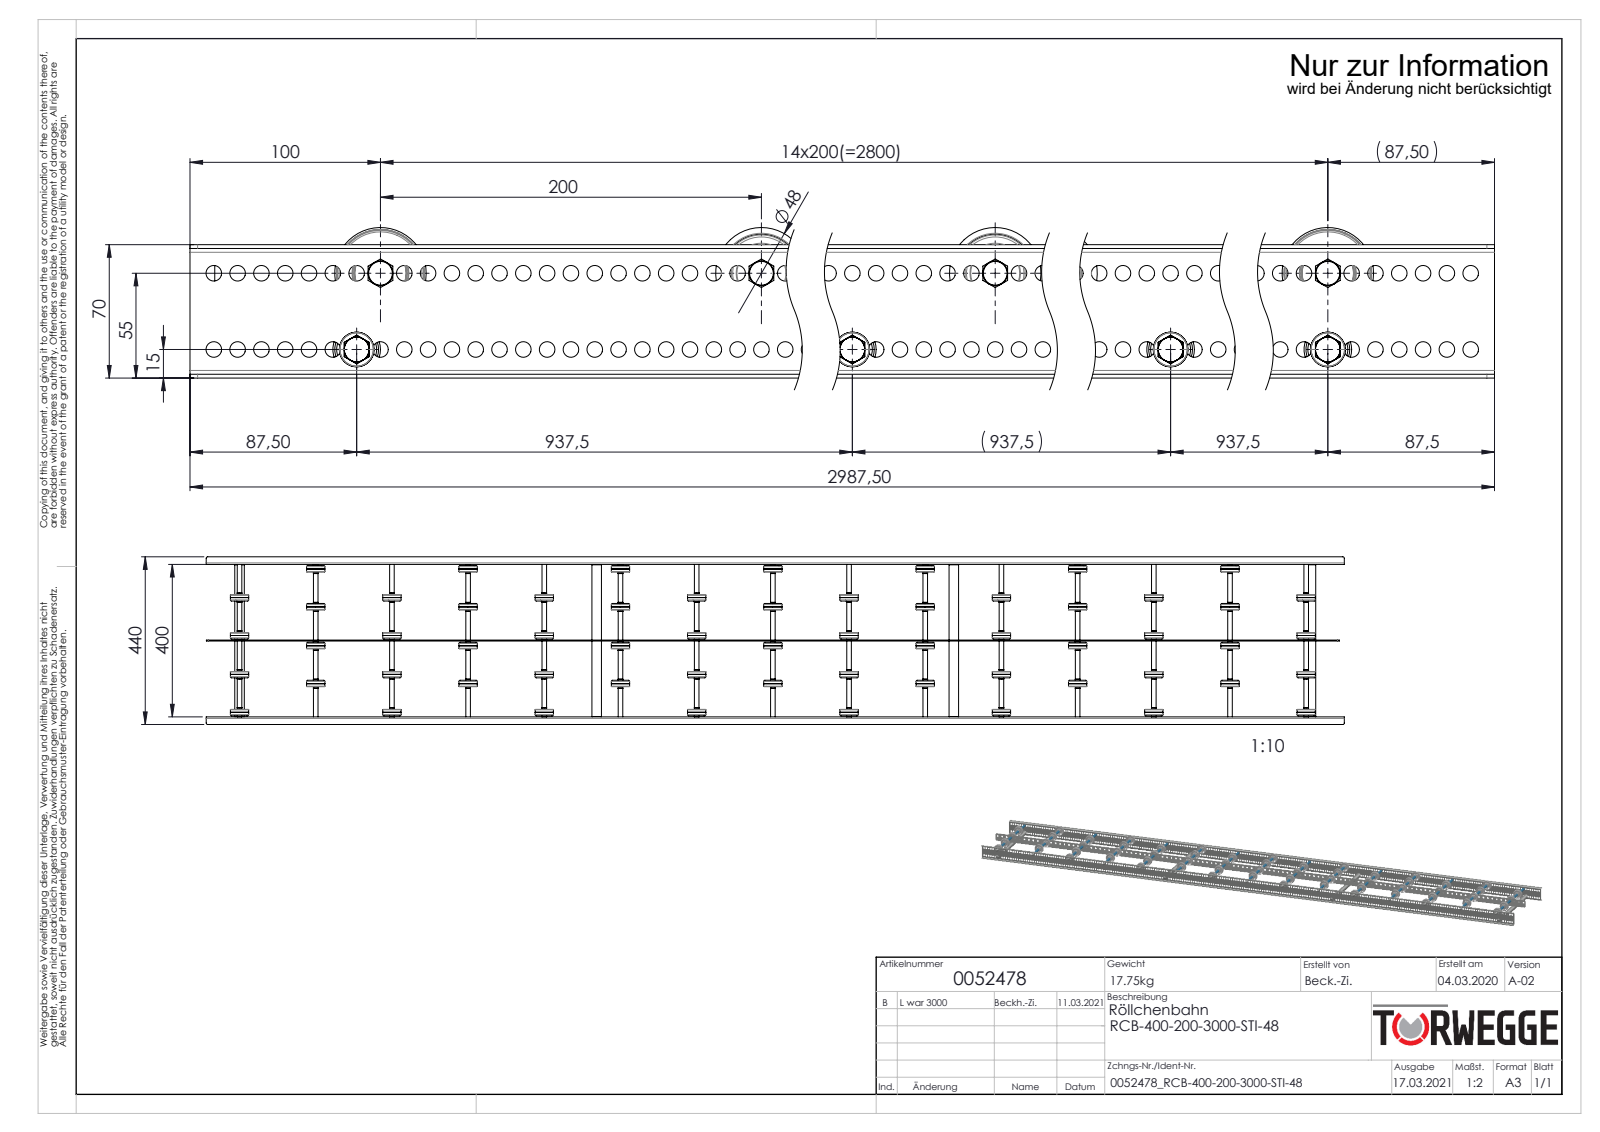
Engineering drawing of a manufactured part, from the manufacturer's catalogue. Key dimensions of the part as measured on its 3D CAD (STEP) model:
Part name (STEP PRODUCT): Profil_LRB-20x70x20x2_KFG_S109080_U-PROFIL-20-70-20-2-LRB-L=2987,5; S100994_Sperrzahnschraube_M08x16-8.8-A2K; Hutmutter_DIN_1587_M8; 0052478 (+6 more)
STEP written by: SolidWorks 2020 (AUTOMOTIVE_DESIGN)
Units: millimetres
Bodies: 248 solids, 8780 faces (1560 planar, 4192 cylindrical, 3028 other)
Overall size (bounding box): 2987.5 × 440 × 79
Volume: 3 504 000 mm³ · Surface area: 2 958 000 mm²
Round holes (diameter × count): ⌀8.2 ×476, ⌀8.5 ×119, ⌀6.65 ×15, ⌀8 ×15, ⌀9.65 ×15, ⌀15 ×15, ⌀41 ×15, ⌀6.8 ×4, ⌀21 ×4
Round bosses / shafts (diameter × count): ⌀48 ×15, ⌀13 ×15, ⌀12.5 ×15, ⌀12.4 ×15, ⌀12 ×15, ⌀11.5 ×15, ⌀25 ×4, ⌀8 ×4
Partial cylindrical surfaces — rounded edges, fillets, slot ends (radius × count): R4 ×8, R2 ×4, R5 ×4
Main face-to-face distances: 2, 402, 201, 201.5, 68, 400, 404, 200.5, 198.5, 203.5
Hole centre spacings: 12.5, 25, 37.5, 50, 62.5, 75, 87.5, 100
